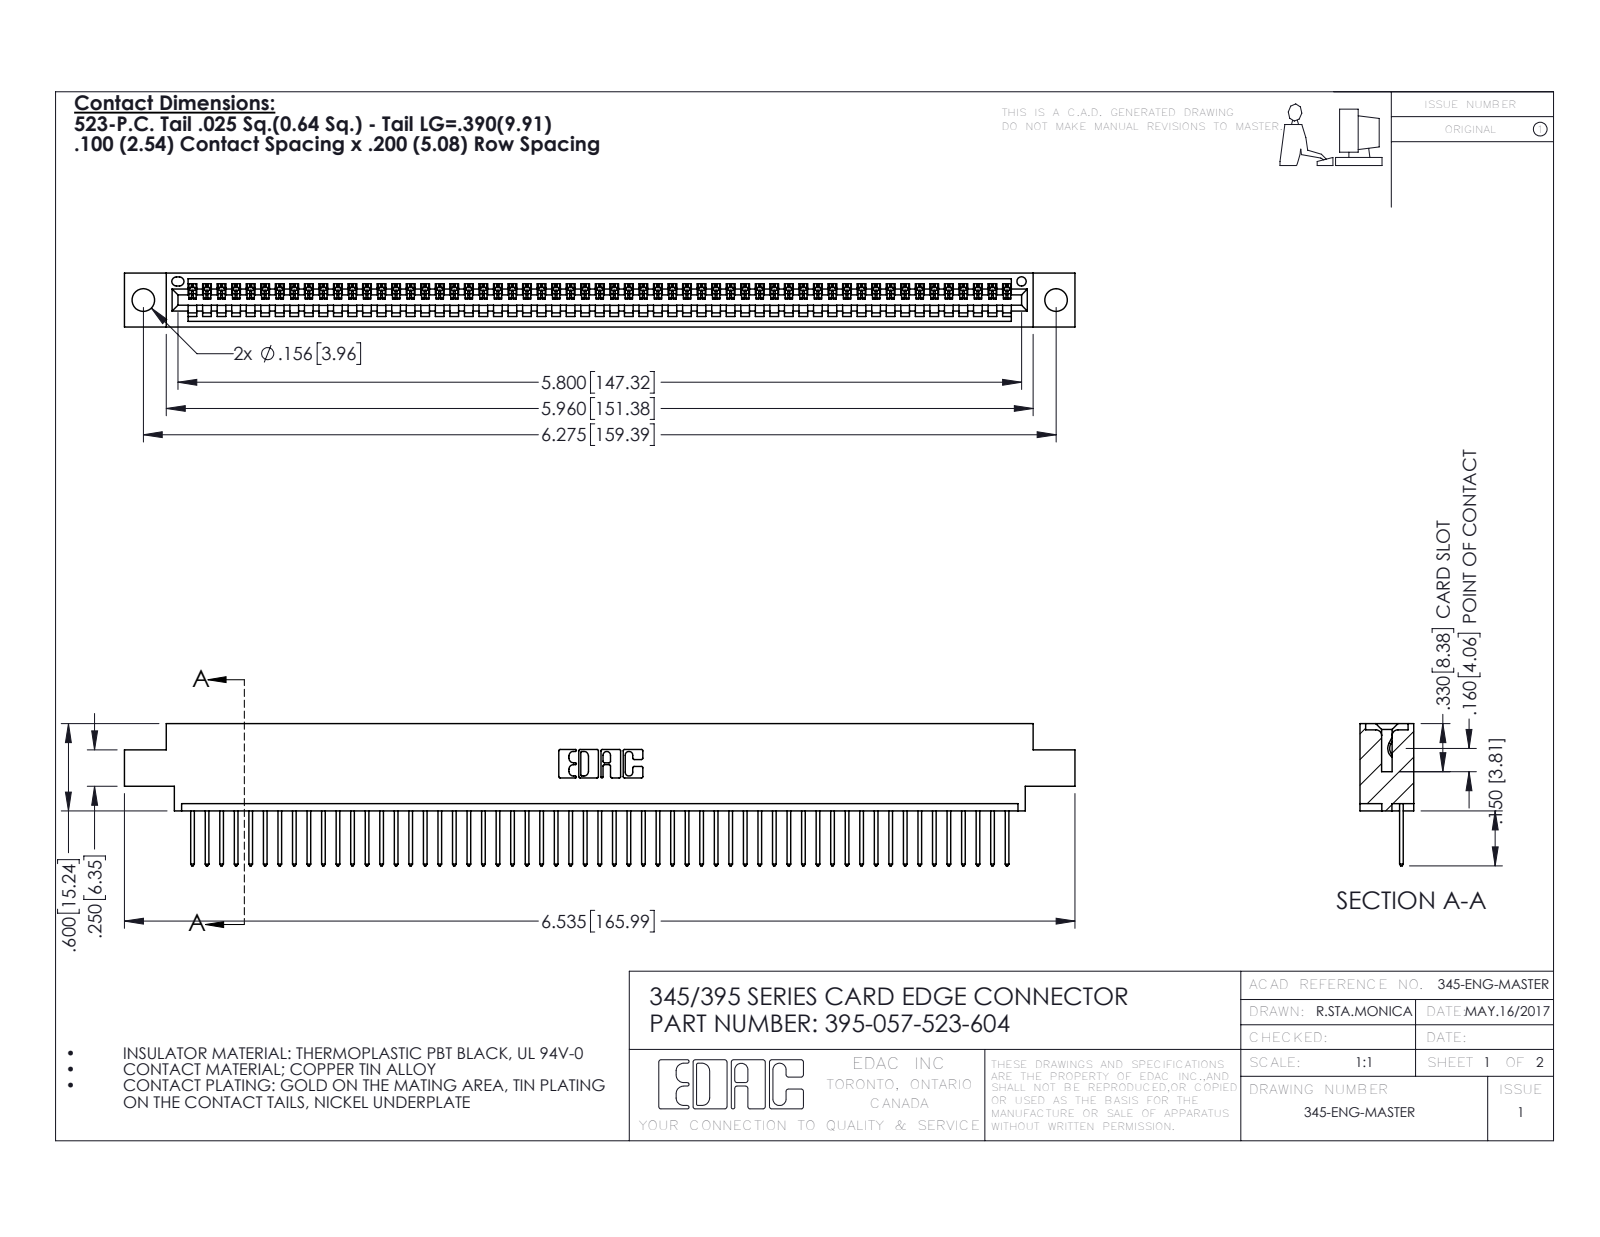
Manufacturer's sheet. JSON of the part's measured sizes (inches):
{"part_name": "395-057-523-604; 345 Part_0.170 Offset - 0.156 Dia-TH; 345-292-001_345-293-123", "step_written_by": "SolidWorks 2016 (CONFIG_CONTROL_DESIGN)", "units": "inches", "bodies": {"solids": 58, "faces": 3436, "planar": 2364, "cylindrical": 1072, "other": 0}, "overall_size": [6.535, 0.977, 0.37], "volume_in3": 0.956, "surface_area_in2": 32.58, "round_holes": [[0.156, 2], [0.064, 1]], "partial_cylinders_radius": [[0.006, 114], [0.01, 114], [0.01, 22], [0.007, 6], [0.031, 6], [0.026, 3], [0.031, 2], [0.04, 2]], "face_to_face_distances": [0.298, 0.072, 0.37, 0.098, 0.272, 0.025, 0.2, 0.225, 0.175, 0.149], "hole_center_spacings": [0.27, 6.039, 6.275]}
